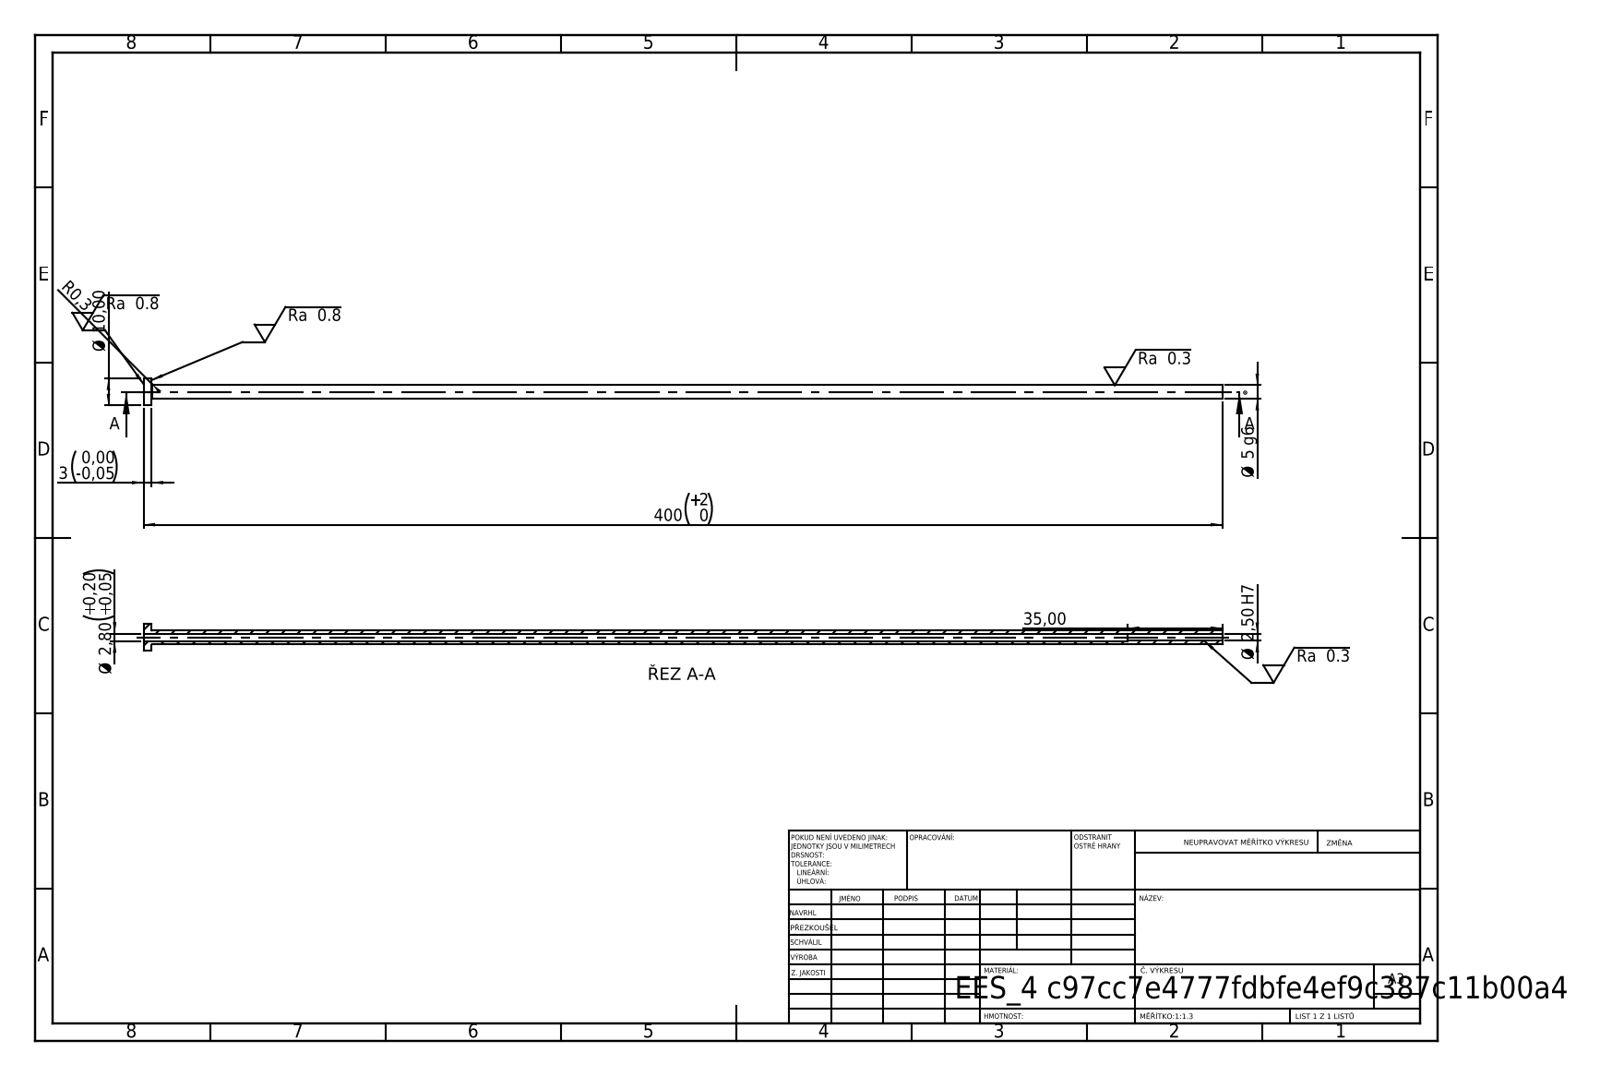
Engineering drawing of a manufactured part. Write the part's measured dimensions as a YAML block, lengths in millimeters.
step_written_by: "SolidWorks 2019 (CONFIG_CONTROL_DESIGN)"
units: millimeters
bodies: {solids: 1, faces: 14, planar: 4, cylindrical: 8, other: 2}
overall_size: [400, 10, 10]
volume: 5612
surface_area: 9961
round_holes:
  - {diameter: 2.5, count: 1}
  - {diameter: 2.8, count: 1}
round_bosses_or_shafts:
  - {diameter: 10, count: 1}
  - {diameter: 5, count: 1}
face_to_face_distances: [3, 400, 397, 365, 362, 35]
